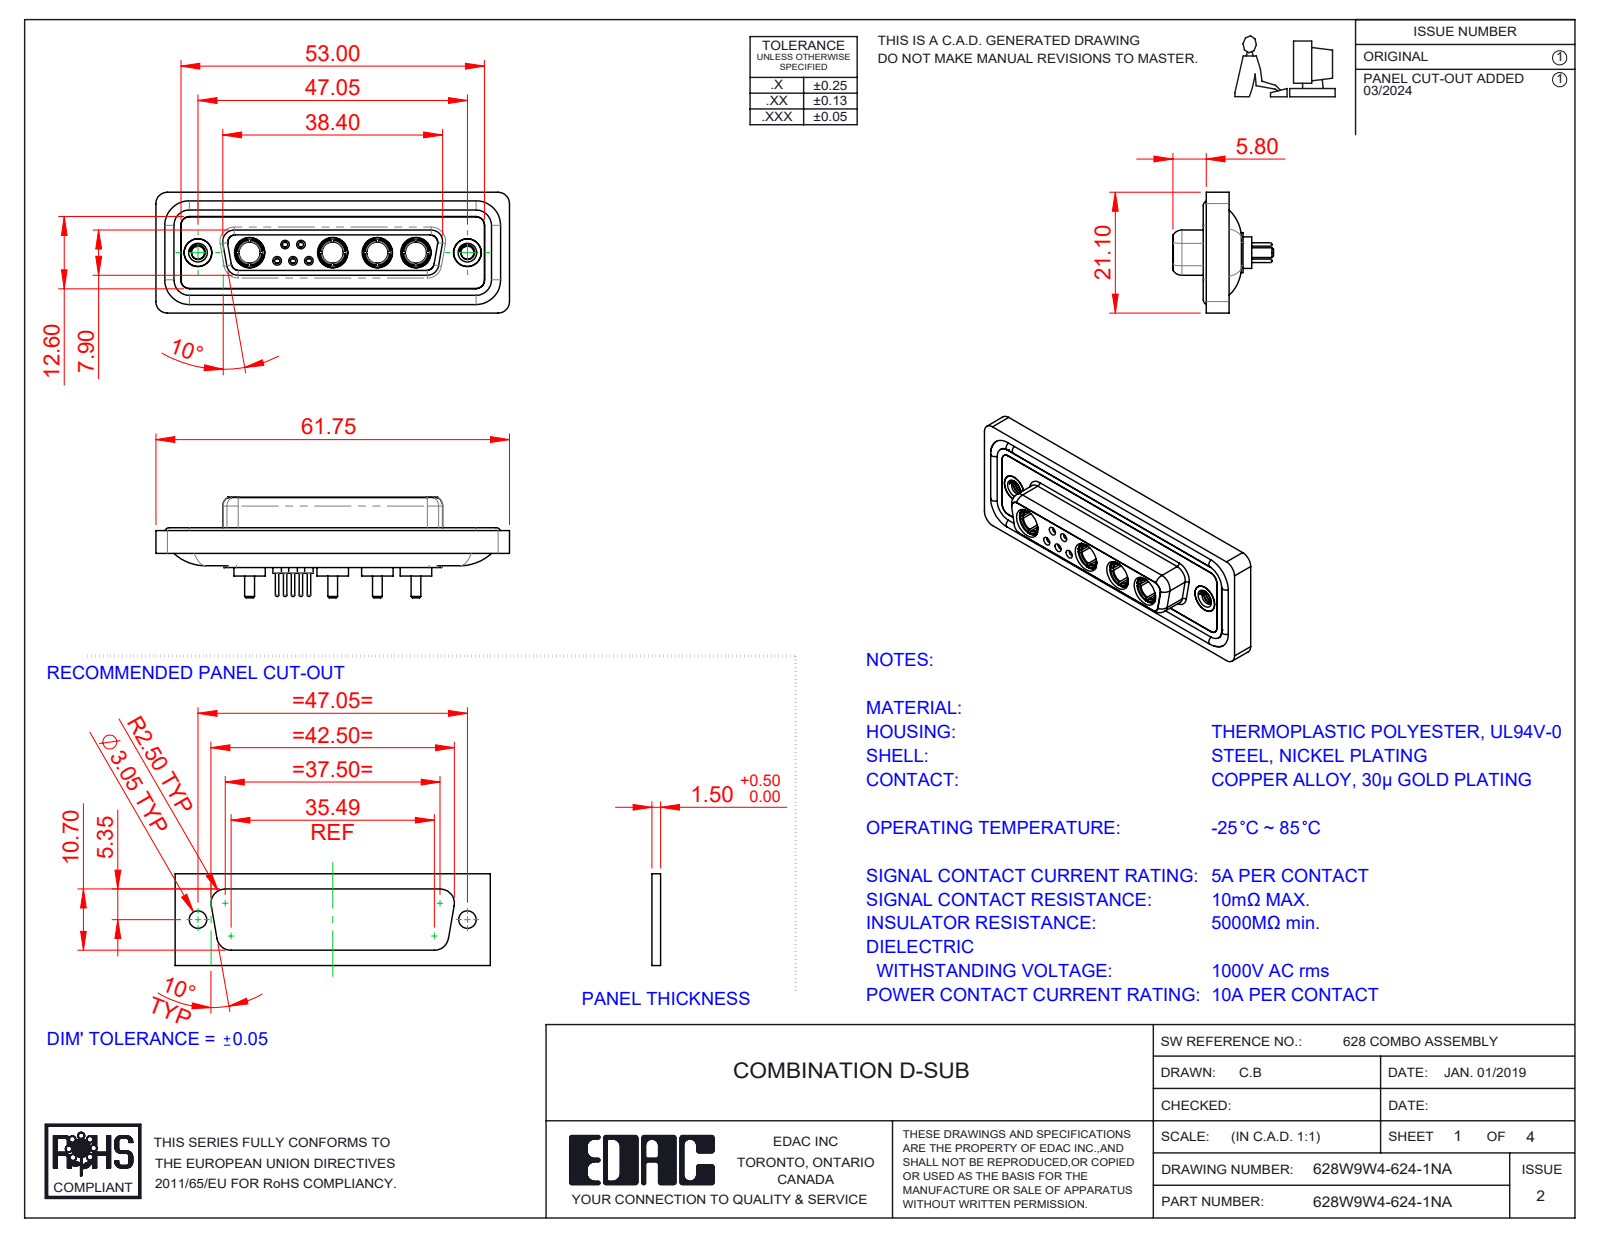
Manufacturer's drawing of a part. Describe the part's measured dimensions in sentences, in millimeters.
The part is named "628W9W4-624-1NA; 628Combo Shell Front_25 Contacts; 628Combo Shell Rear_25 Contacts; 628Combo Threaded Rivet_A (+5 more)". Its 3-D file was written by "SolidWorks 2023 (CONFIG_CONTROL_DESIGN)". It is 20 solids with 955 faces: 296 planar, 377 cylindrical and 282 other. Overall it measures 61.75 by 21.1 by 17.55 millimeters. Its volume is 8 166 cubic millimeters and its surface area 13 509 square millimeters. Round holes: 6 of diameter 4.85, 5 of diameter 0.9, 5 of diameter 1.1, 5 of diameter 1.5, 5 of diameter 2, 4 of diameter 3.7, 4 of diameter 5.3, 3 of diameter 1.6, 2 of diameter 1.7, 2 of diameter 2.26, 2 of diameter 4, 2 of diameter 4.05. Round bosses or shafts: 6 of diameter 1.6, 5 of diameter 2.2, 5 of diameter 0.6, 4 of diameter 5.5, 4 of diameter 5.2, 4 of diameter 4.96, 4 of diameter 4.75, 4 of diameter 3.75. Partial cylindrical surfaces (rounded edges, fillets, slot ends): 22 of radius 1.5, 18 of radius 2, 8 of radius 1.35, 8 of radius 1.6, 4 of radius 0.25, 4 of radius 0.5, 4 of radius 0.6, 4 of radius 0.65. The main face-to-face distances are 0.4, 1.8, 7.45, 5.65, 0.5, 7.05, 6.6, 1.6, 1.1, 2.9. The hole center spacings are 3.16, 2.77, 5.03, 2.76, 4.4, 5.02, 5.54, 5.73.
